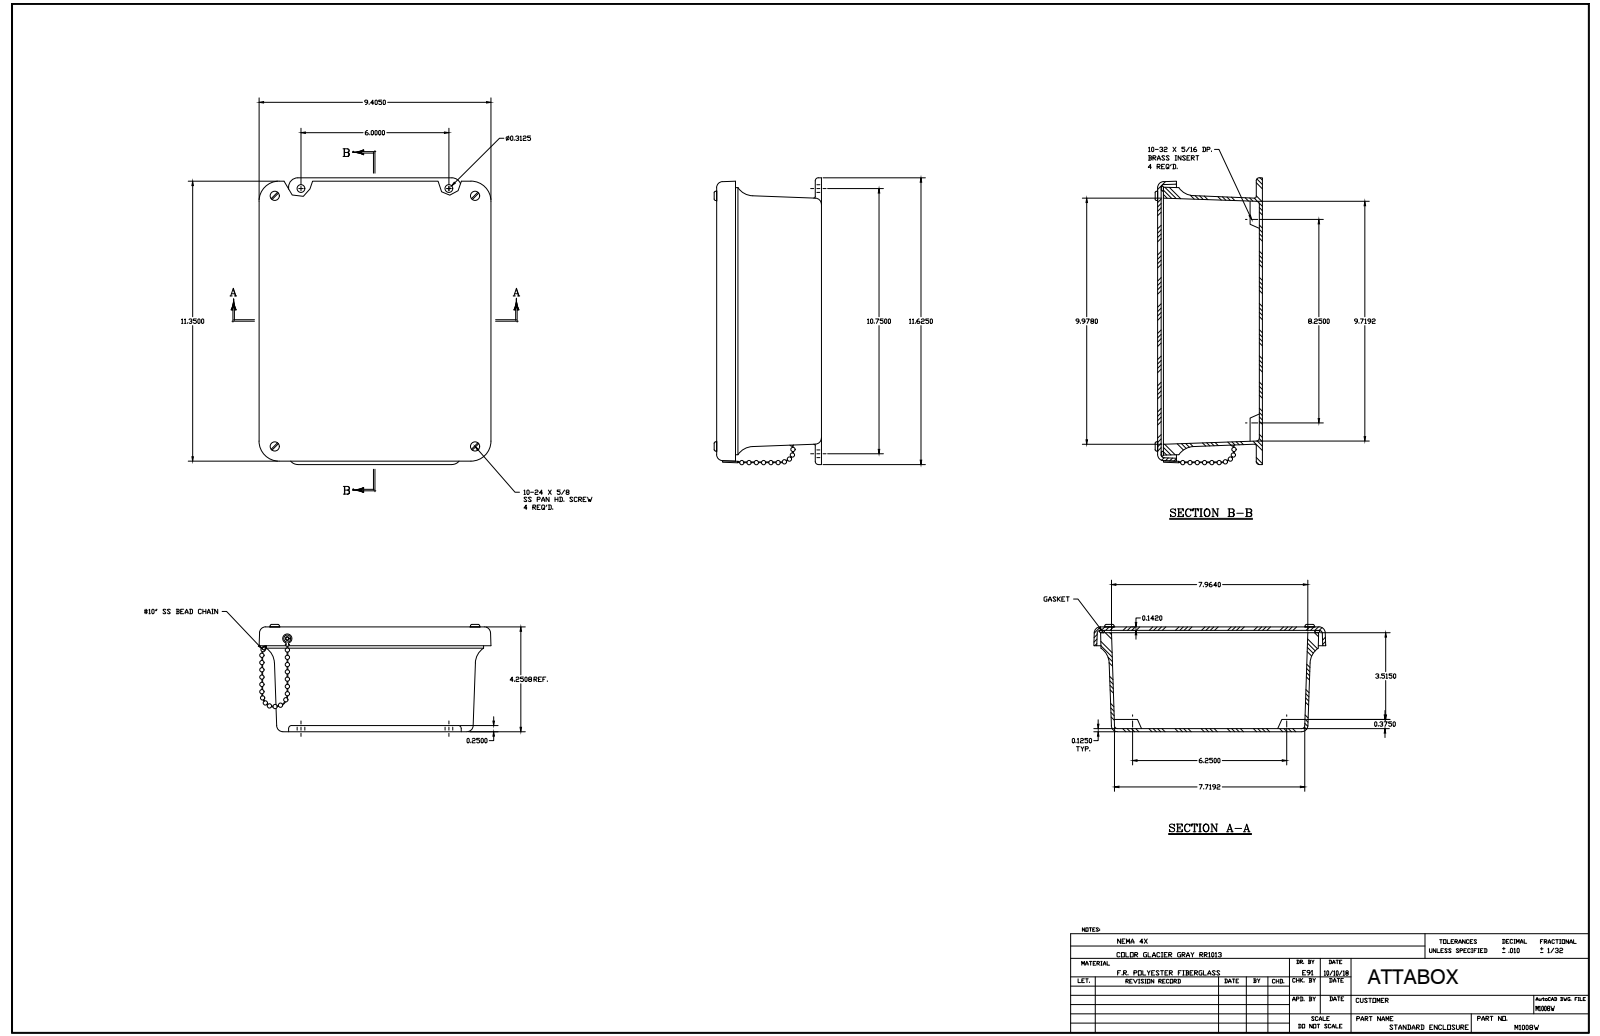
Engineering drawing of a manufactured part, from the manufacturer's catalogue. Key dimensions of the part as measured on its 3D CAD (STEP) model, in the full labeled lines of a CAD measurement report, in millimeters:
Part name (STEP PRODUCT): M1008W
STEP written by: SolidWorks 2018 (AUTOMOTIVE_DESIGN)
Units: millimetres
Bodies: 45 solids, 887 faces (187 planar, 287 cylindrical, 413 other)
Overall size (bounding box): 306 × 244.8 × 110.5
Volume: 986 000 mm³ · Surface area: 503 300 mm²
Round holes (diameter × count): ⌀3.6 ×5, ⌀3.9 ×5, ⌀3.7 ×4, ⌀4 ×4, ⌀5.5 ×4, ⌀4.7 ×2, ⌀3.2 ×1
Round bosses / shafts (diameter × count): ⌀6.9 ×8, ⌀4.8 ×4, ⌀4 ×4, ⌀6.4 ×2, ⌀9.5 ×1, ⌀9.5 ×1, ⌀7.2 ×1, ⌀3.2 ×1
Partial cylindrical surfaces — rounded edges, fillets, slot ends (radius × count): R0.8 ×20, R3.2 ×12, R5.1 ×8, R6.4 ×8, R9.5 ×4, R19.1 ×4, R0.3 ×2, R1.6 ×2
Main face-to-face distances: 3.6, 103.6, 107.2, 3.2, 100.4, 104, 98.8, 5.2, 102, 1.6
Hole centre spacings: 34, 63.5, 152.4, 158.8, 184.2, 184.2, 206.4, 209.6
